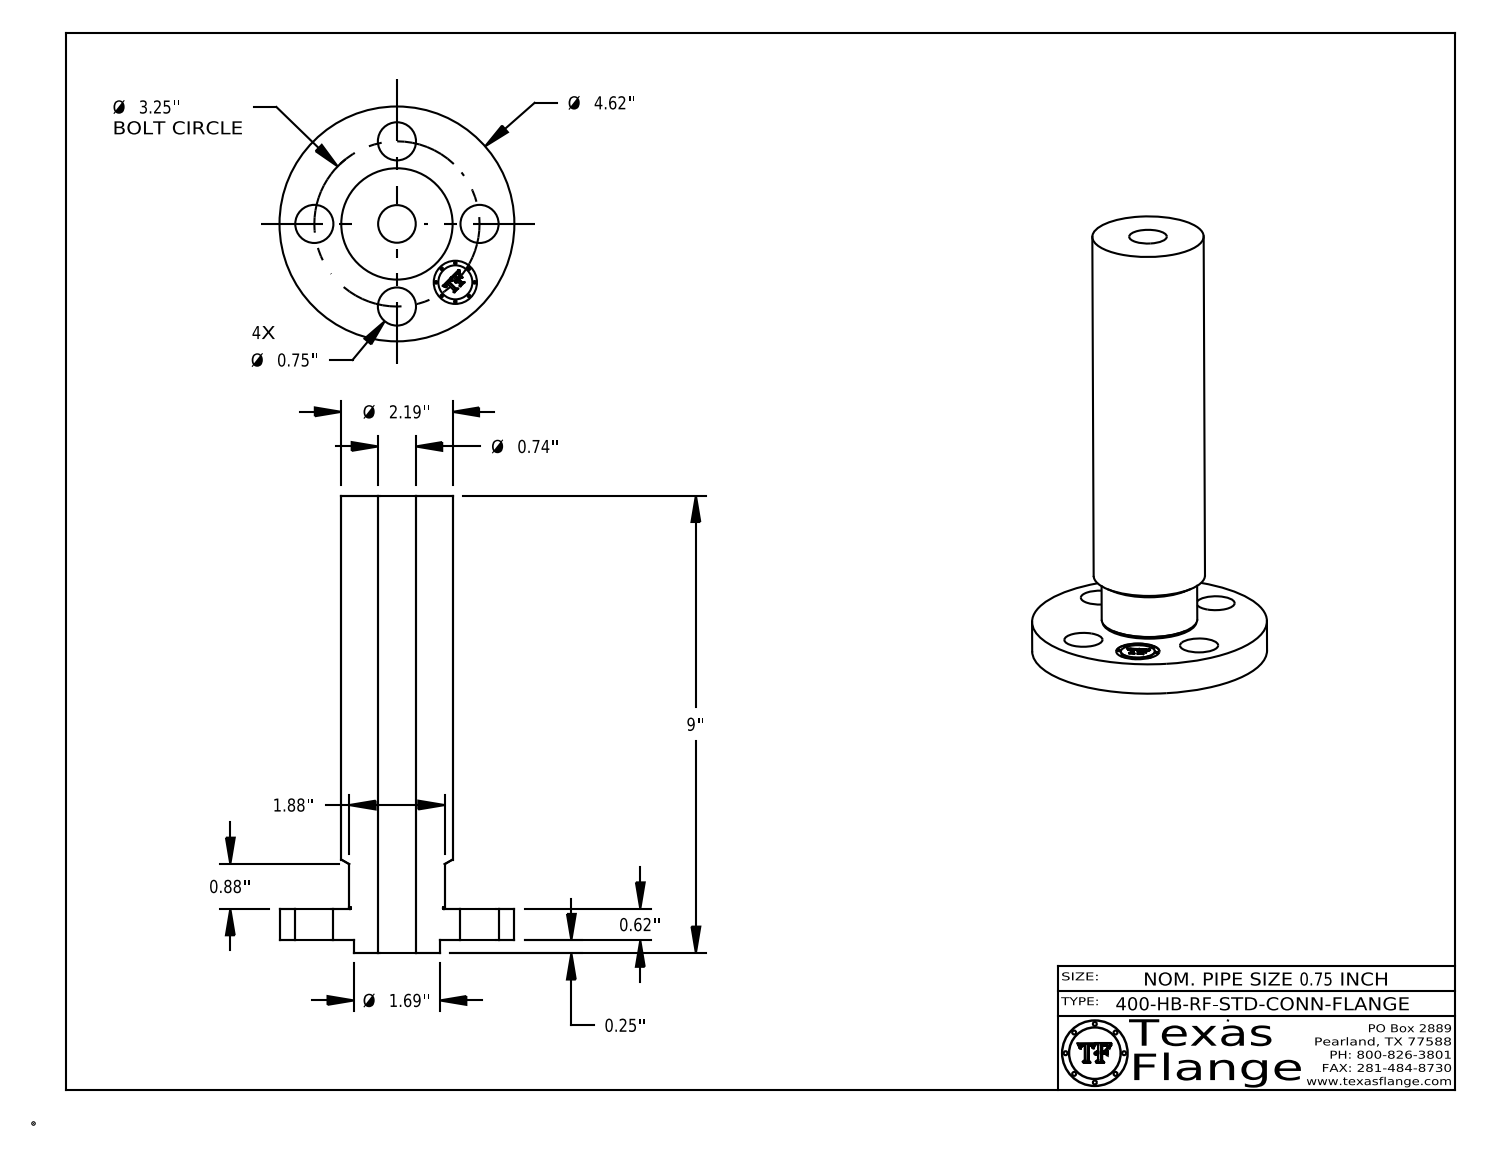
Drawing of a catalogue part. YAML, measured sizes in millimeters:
part_name: "0.75-400-HB-RF-STD-CONN-FLANGE"
step_written_by: "CATIA V5 STEP AP214 (AUTOMOTIVE_DESIGN)"
units: millimeters
bodies: {solids: 1, faces: 413, planar: 369, cylindrical: 38, other: 6}
overall_size: [228.6, 117.3, 117.3]
volume: 584900
surface_area: 79420
round_holes:
  - {diameter: 19.1, count: 4}
  - {diameter: 18.8, count: 1}
  - {diameter: 21.6, count: 1}
round_bosses_or_shafts:
  - {diameter: 1.3, count: 8}
  - {diameter: 117.3, count: 1}
  - {diameter: 55.6, count: 1}
  - {diameter: 47.8, count: 1}
  - {diameter: 42.9, count: 1}
  - {diameter: 17, count: 1}
face_to_face_distances: [15.7, 222.3, 206.5, 6.4, 22.1, 228.6, 22, 15.6, 206.6, 6.5]
hole_center_spacings: [41.3, 58.4, 31.6, 76.3, 82.6]
